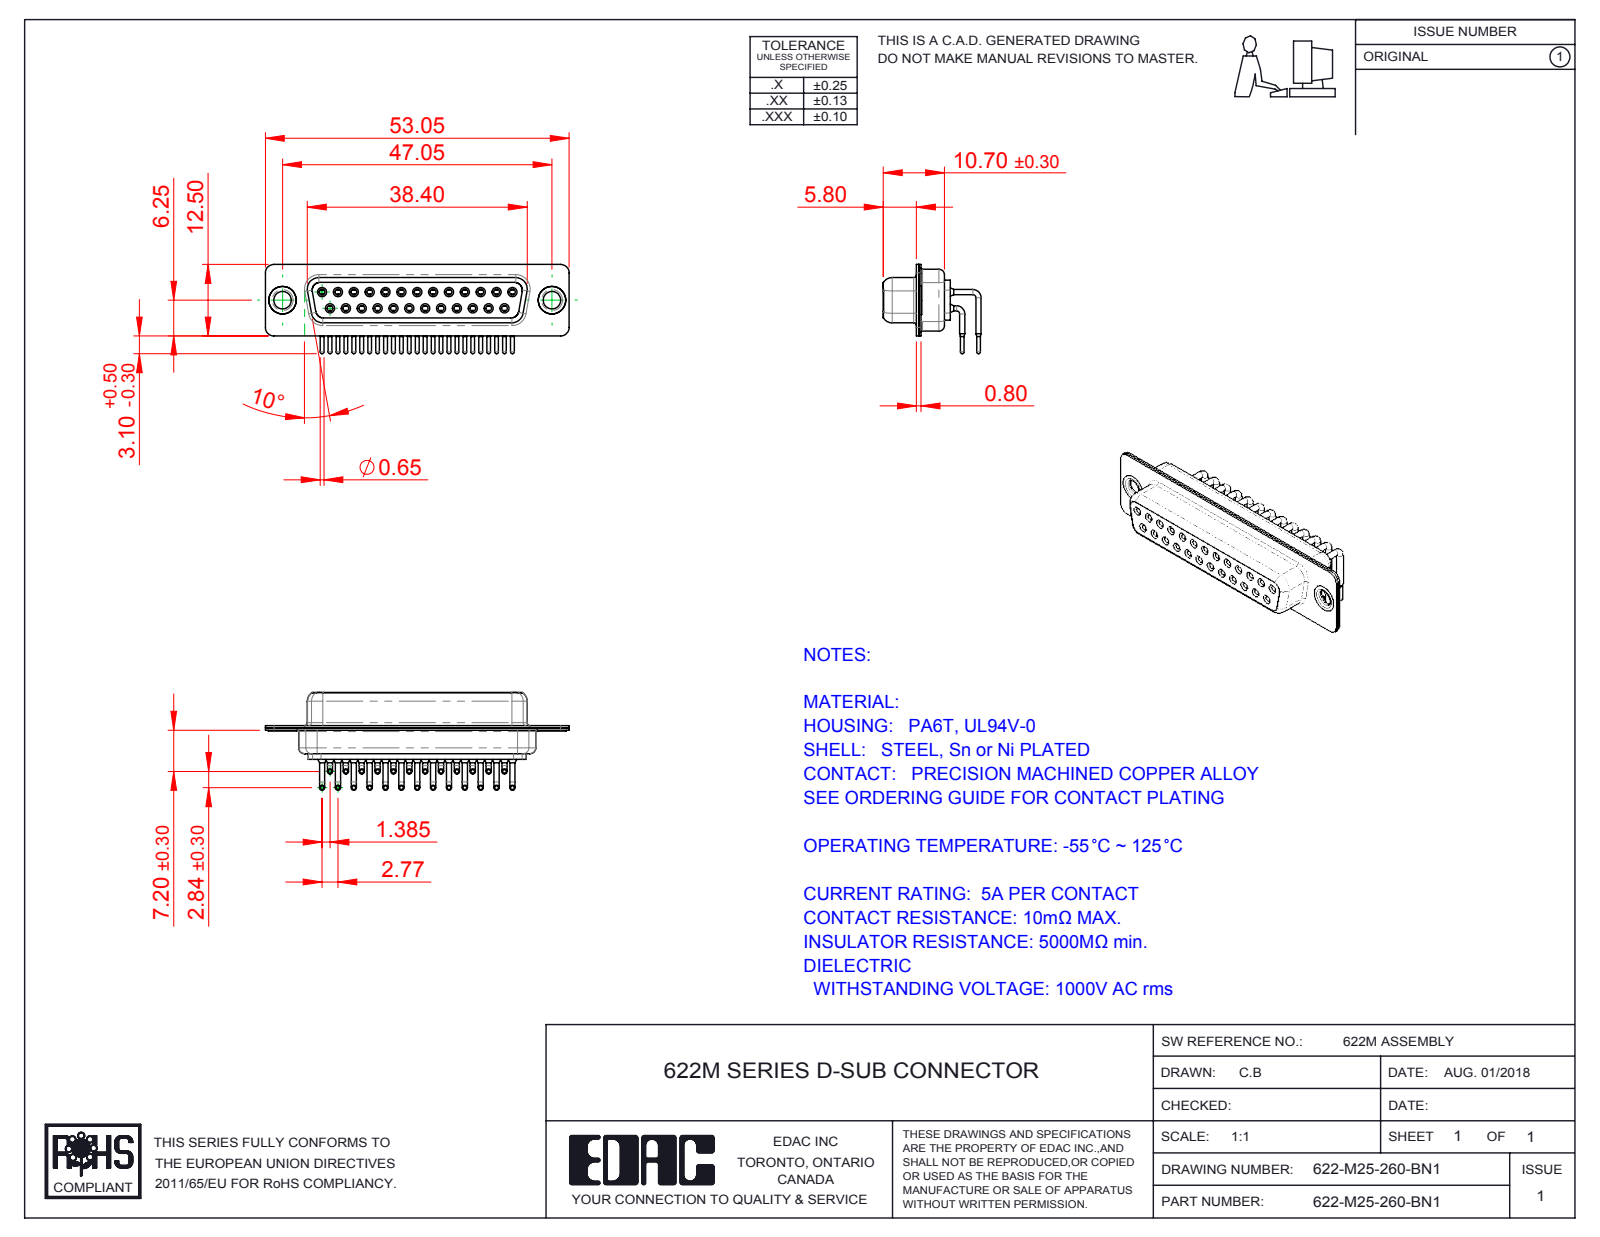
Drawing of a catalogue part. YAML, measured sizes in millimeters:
part_name: "622M Contact Row 2; 622M Thru Hole Rivet; 622-M25-260-BN1; 622M Shell Rear_25 Contacts (+3 more)"
step_written_by: "SolidWorks 2016 (CONFIG_CONTROL_DESIGN)"
units: millimeters
bodies: {solids: 30, faces: 1578, planar: 442, cylindrical: 696, other: 440}
overall_size: [53.05, 17.09, 15.6]
volume: 3773
surface_area: 9352
round_holes:
  - {diameter: 1, count: 25}
  - {diameter: 1.1, count: 25}
  - {diameter: 1.7, count: 25}
  - {diameter: 1.8, count: 25}
  - {diameter: 2, count: 25}
  - {diameter: 3.05, count: 2}
  - {diameter: 4, count: 2}
  - {diameter: 4.8, count: 2}
round_bosses_or_shafts:
  - {diameter: 0.9, count: 50}
  - {diameter: 1.6, count: 25}
  - {diameter: 1.5, count: 25}
  - {diameter: 0.65, count: 25}
  - {diameter: 5, count: 2}
  - {diameter: 4.9, count: 2}
  - {diameter: 3.55, count: 2}
partial_cylinders:
  - {radius: 1.5, count: 16}
  - {radius: 2, count: 12}
  - {radius: 1.35, count: 8}
  - {radius: 1.6, count: 8}
  - {radius: 0.25, count: 4}
  - {radius: 0.5, count: 4}
  - {radius: 0.6, count: 4}
  - {radius: 0.65, count: 4}
face_to_face_distances: [0.4, 1.45, 8.95, 6.2, 1.9, 8.5, 0.45, 7.05, 2.3, 0.85]
hole_center_spacings: [3.16, 2.77, 5.54, 8.31, 11.08, 13.85, 16.62, 5.03]
